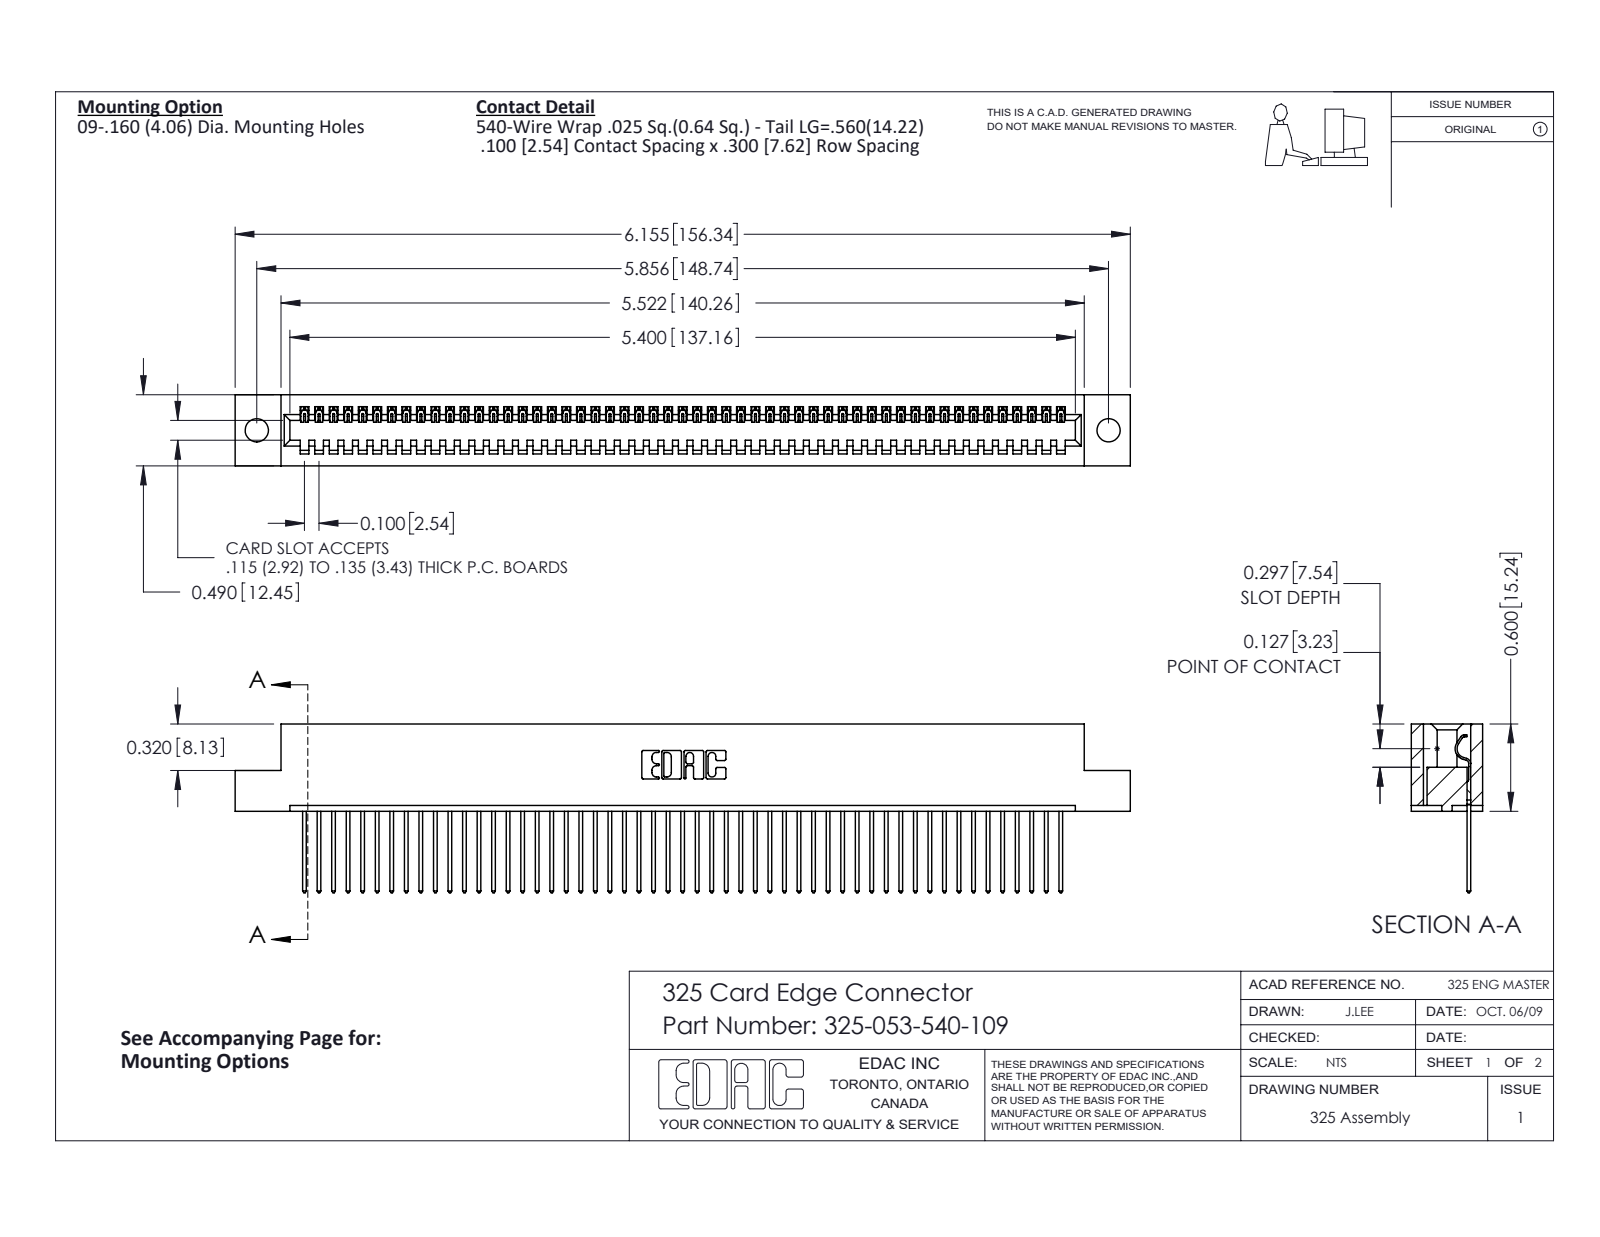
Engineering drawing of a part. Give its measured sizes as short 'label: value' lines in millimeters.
name: 325 Part_.160 TH; 325-053-540-109; 325-292-001_325-293-140
written by: SolidWorks 2016 (CONFIG_CONTROL_DESIGN)
unit: mm
bodies: 54 solids, 3188 faces (2296 planar, 892 cylindrical, 0 other)
size: 156.3 × 29.5 × 12.4
volume: 19 780 mm³; area: 22 220 mm²
holes: 2× ⌀4.1
rounds: 106× R0.2, 106× R0.3, 22× R0.3, 6× R0.2, 6× R0.8, 3× R0.7, 1× R0.4, 1× R0.6
face distances: 2.1, 10.3, 12.4, 7.6, 2.7, 9.7, 0.6, 8.3, 14.2, 6.7
hole spacings: 148.7
